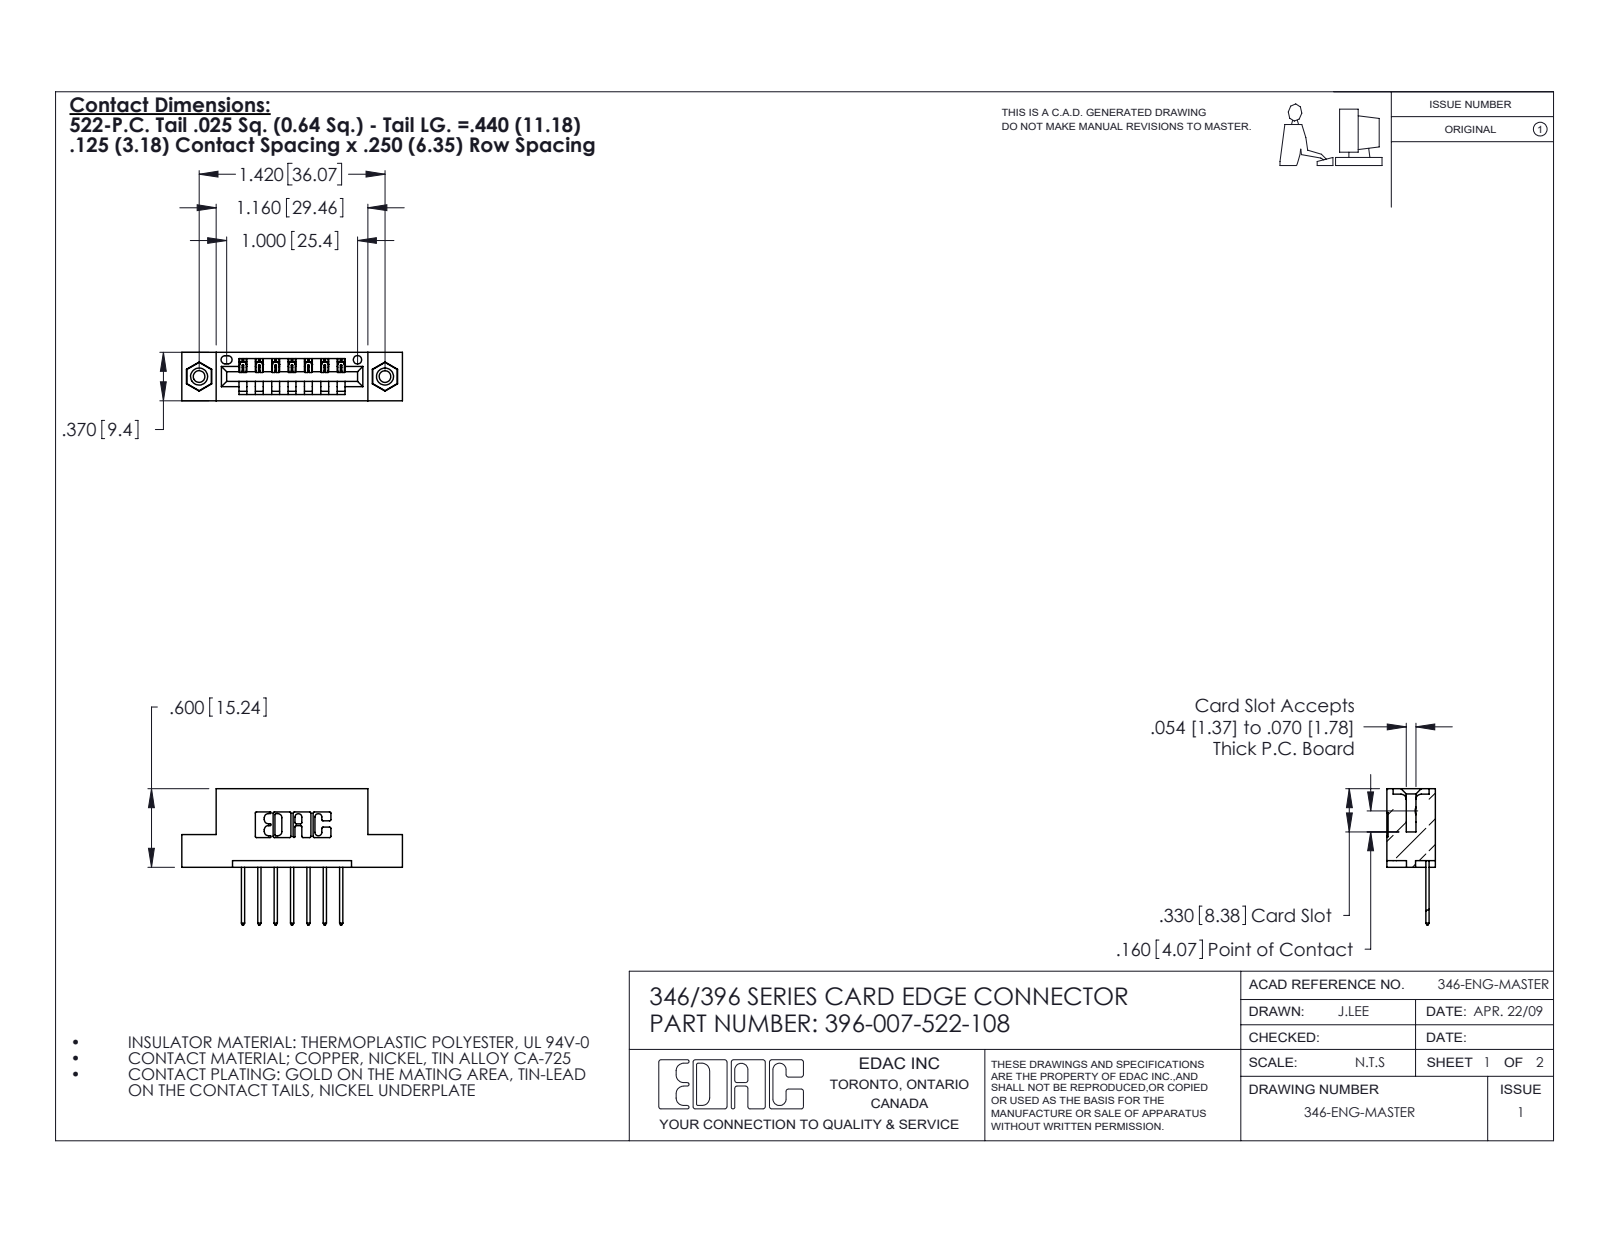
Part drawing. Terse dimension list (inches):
name: 345-292-001_345-293-122; 396-007-522-108; 345-250-001_345-250-003-102; 346 Part_Flush Mounting Lugs - 0.156 Dia-TI
written by: SolidWorks 2020 (CONFIG_CONTROL_DESIGN)
unit: in
bodies: 10 solids, 588 faces (388 planar, 184 cylindrical, 16 other)
size: 1.685 × 1.04 × 0.37
volume: 0.235 in³; area: 6.947 in²
holes: 2× ⌀0.089, 2× ⌀0.125, 2× ⌀0.156, 1× ⌀0.064
bosses: 2× ⌀0.155
rounds: 22× R0.01, 14× R0.006, 14× R0.01, 6× R0.007, 6× R0.031, 3× R0.026, 2× R0.031, 2× R0.04
face distances: 0.25, 0.37, 0.048, 0.322, 0.072, 0.298, 0.025, 0.148, 0.222, 0.1
hole spacings: 0.246, 1.217, 1.42
